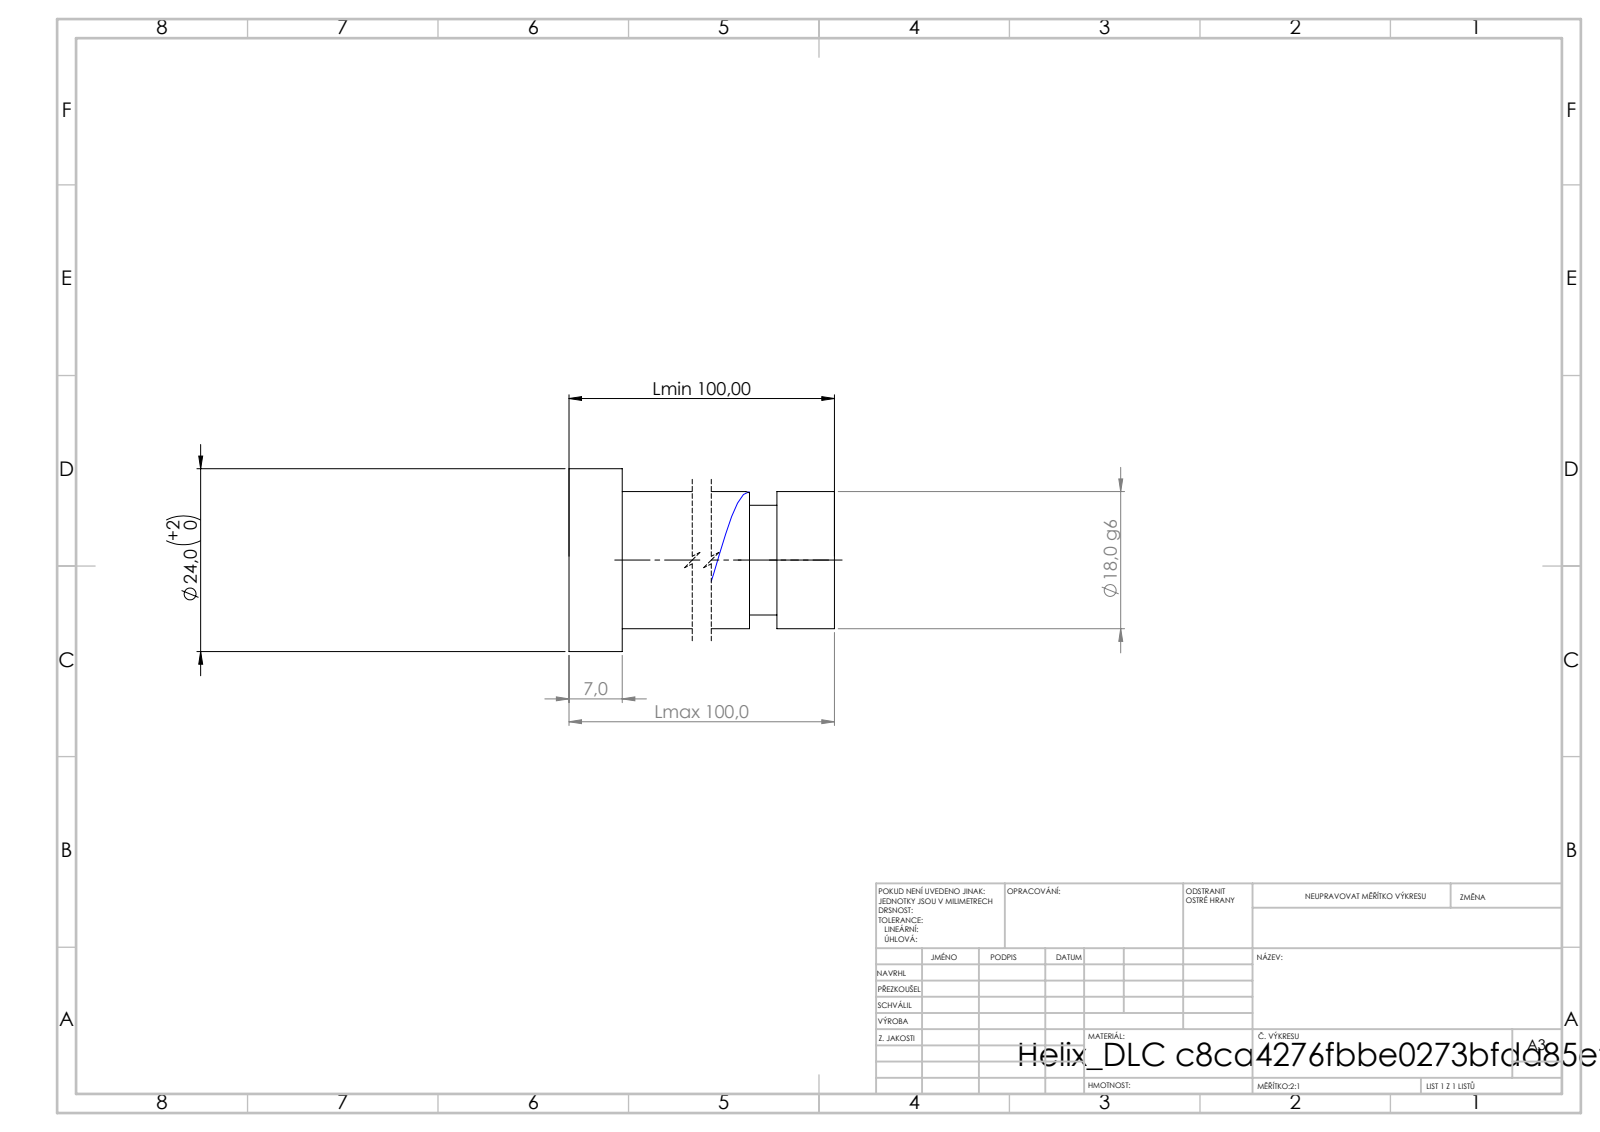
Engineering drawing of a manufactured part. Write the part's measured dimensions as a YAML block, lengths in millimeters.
step_written_by: "SolidWorks 2019 (CONFIG_CONTROL_DESIGN)"
units: millimeters
bodies: {solids: 1, faces: 21, planar: 6, cylindrical: 14, other: 1}
overall_size: [100, 24, 24]
volume: 26259
surface_area: 7283
round_bosses_or_shafts:
  - {diameter: 24, count: 1}
  - {diameter: 18, count: 1}
  - {diameter: 14.4, count: 1}
face_to_face_distances: [100, 7, 93, 92.45, 85.45, 7.55, 88.85, 81.85, 3.6, 11.15]
